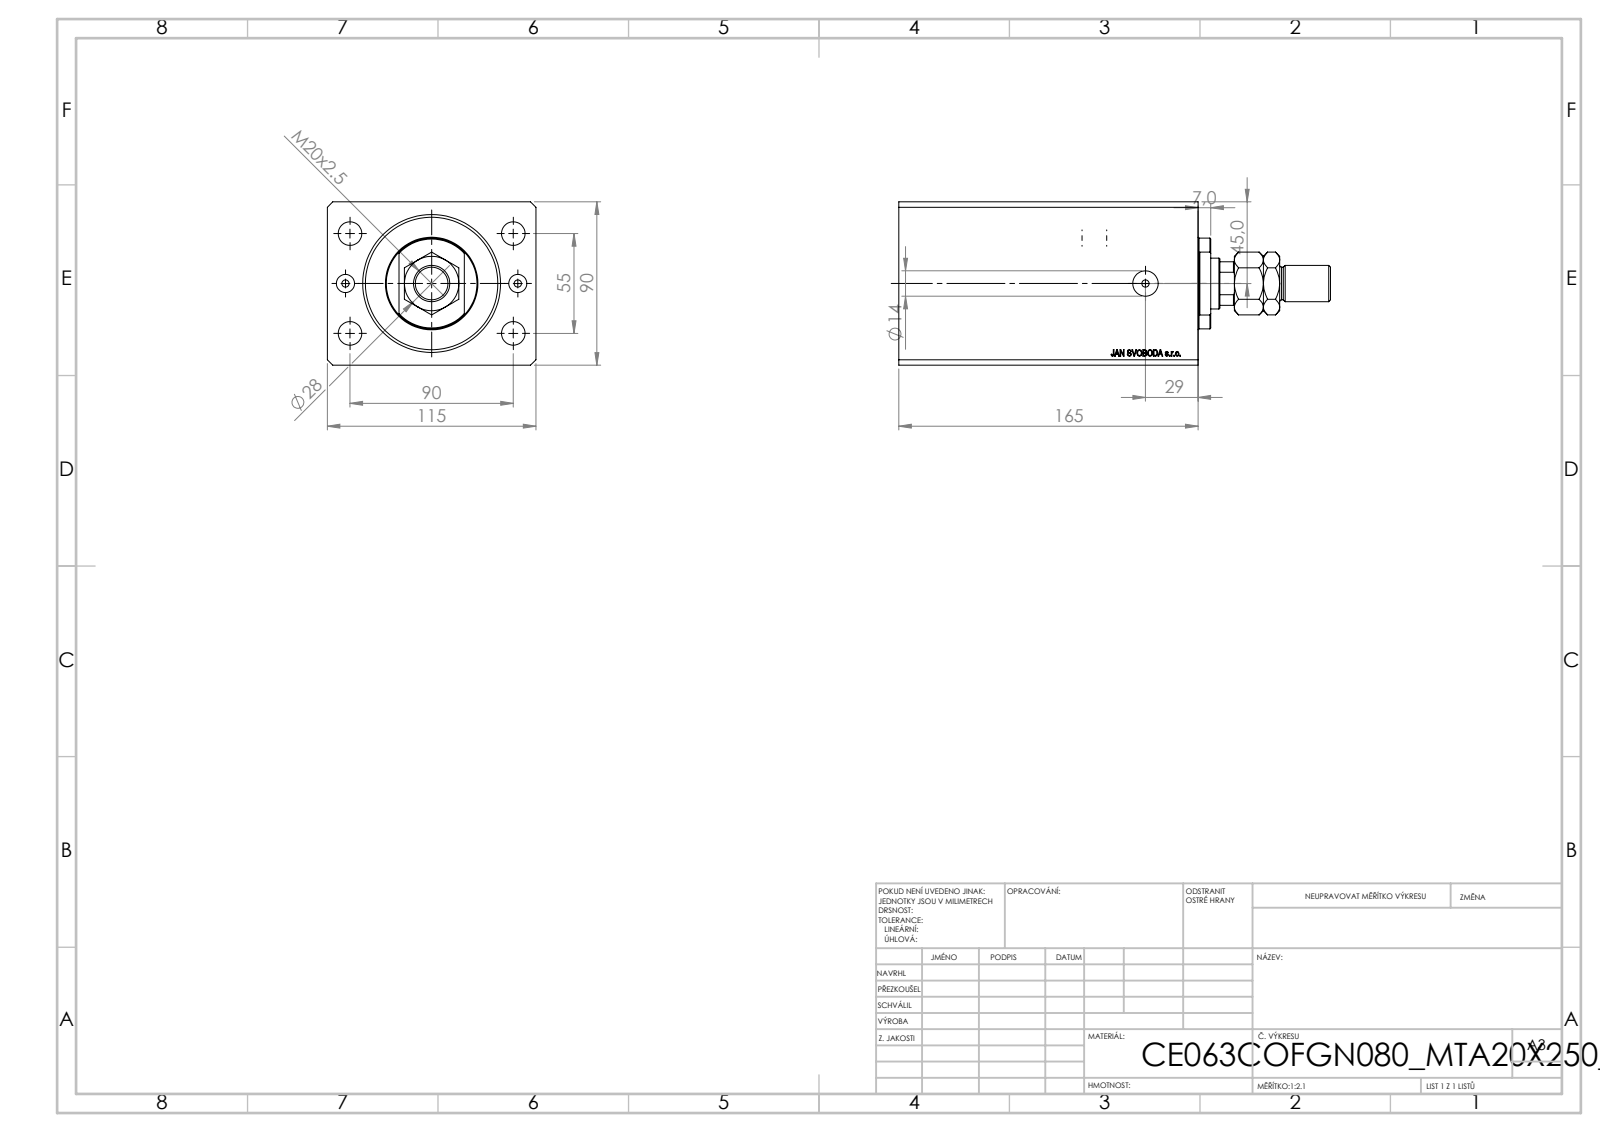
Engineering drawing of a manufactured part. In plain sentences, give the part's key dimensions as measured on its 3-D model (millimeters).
The part is named "MTA; V250CE_VC_C; V250CE_C_Body; V250CE_C_VCP". Its 3-D file was written by "SolidWorks 2019 (CONFIG_CONTROL_DESIGN)". It is 4 solids with 913 faces: 443 planar, 48 cylindrical and 422 other. Overall it measures 237.9 by 115 by 90 millimeters. Its volume is 1 451 000 cubic millimeters and its surface area 197 546 square millimeters. Round holes: 4 of diameter 4, 4 of diameter 13, 2 of diameter 10, 2 of diameter 14, 1 of diameter 18.5, 1 of diameter 28, 1 of diameter 63, 1 of diameter 76. Round bosses or shafts: 1 of diameter 50, 1 of diameter 20, 1 of diameter 18. Partial cylindrical surfaces (rounded edges, fillets, slot ends): 1 of radius 13.5. The main face-to-face distances are 90, 115, 165, 17.9, 147.1, 134.9, 117, 30.1, 54.9, 80. The hole center spacings are 27.61, 52.74, 96.5, 47.5, 55, 90, 105.48, 95.
